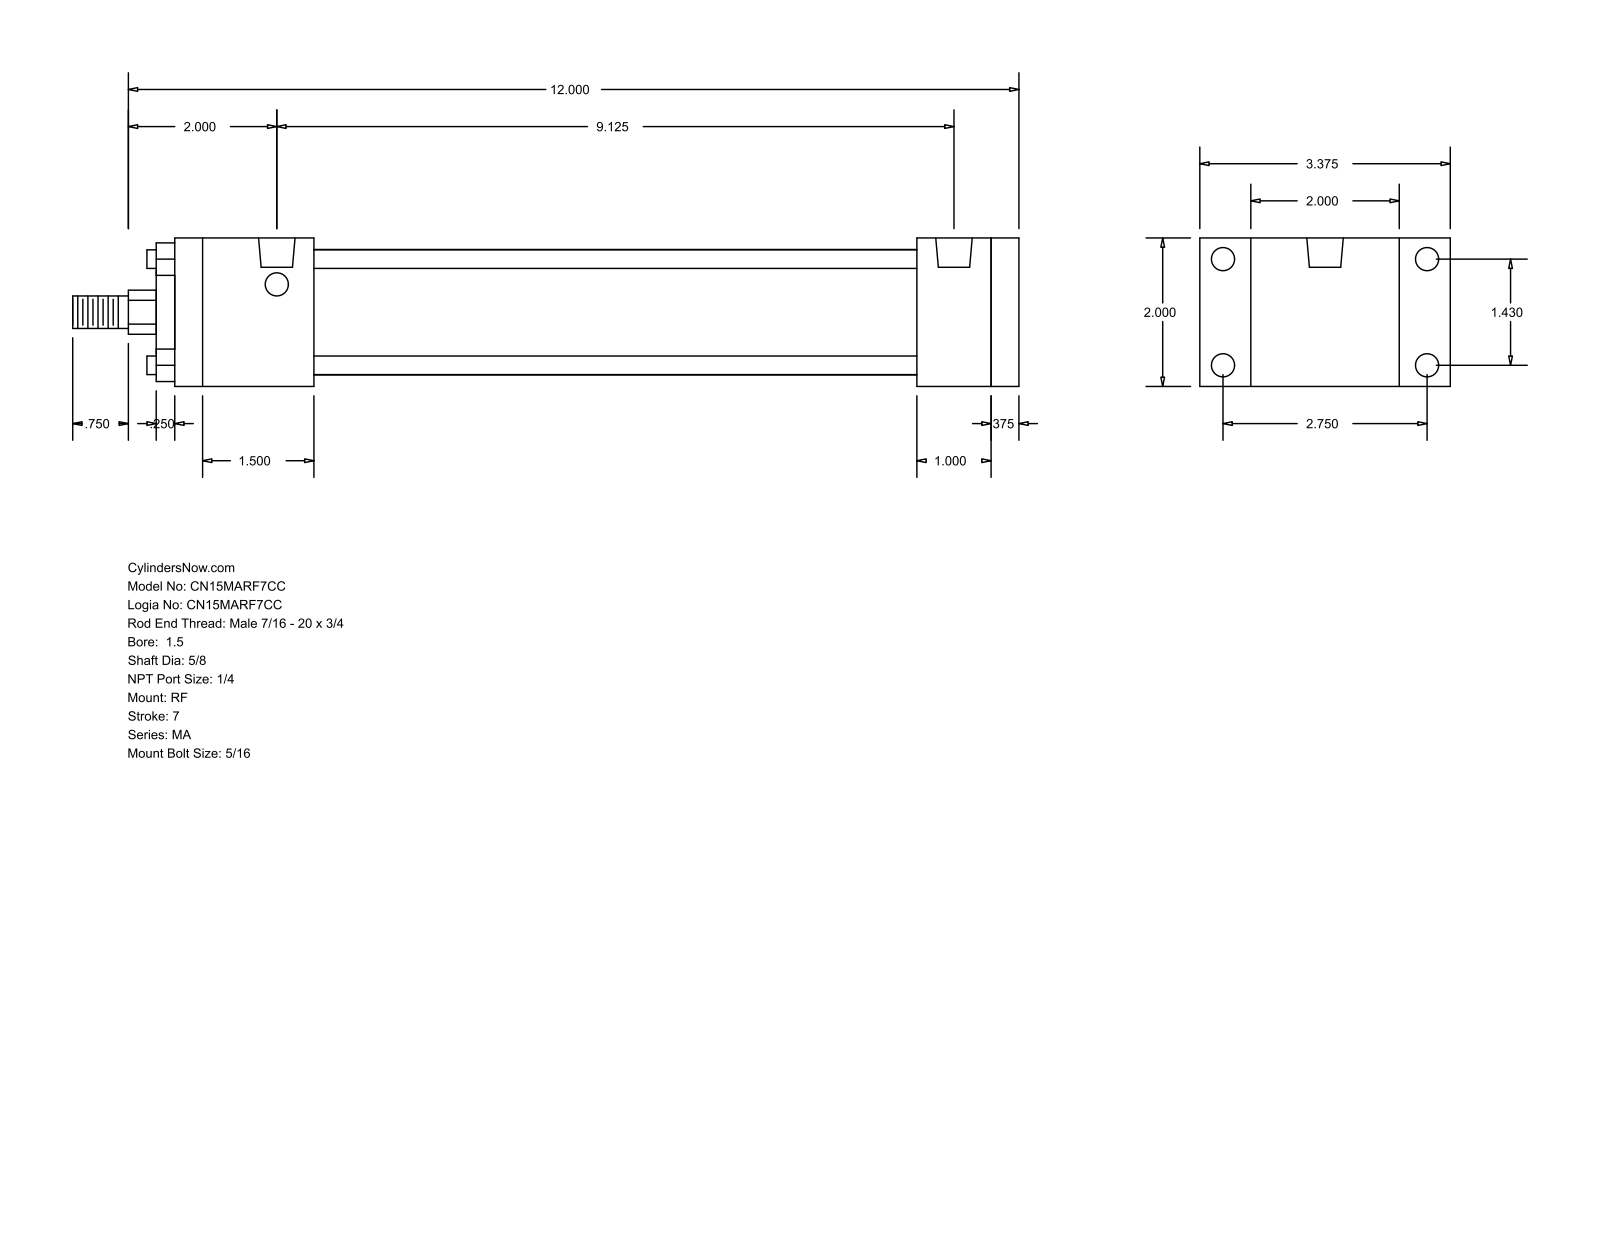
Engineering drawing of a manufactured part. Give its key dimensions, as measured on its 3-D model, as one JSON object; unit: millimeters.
{"part_name": "MA_RF__0150_0.625", "step_written_by": "GSSL Pune (CONFIG_CONTROL_DESIGN)", "units": "millimeters", "bodies": {"solids": 0, "faces": 92, "planar": 64, "cylindrical": 28, "other": 0}, "overall_size": [323.85, 85.72, 50.8], "round_holes": [[7.94, 8], [12.49, 2]], "round_bosses_or_shafts": [[6.35, 4], [42.93, 1], [28.57, 1], [15.88, 1], [11.11, 1]], "partial_cylinders_radius": [[7.54, 1]], "face_to_face_distances": [50.8, 9.53, 288.92, 279.39, 254, 25.39, 34.92, 47.62, 206.38, 231.77], "hole_center_spacings": [36.32, 69.84, 78.72, 231.77]}
